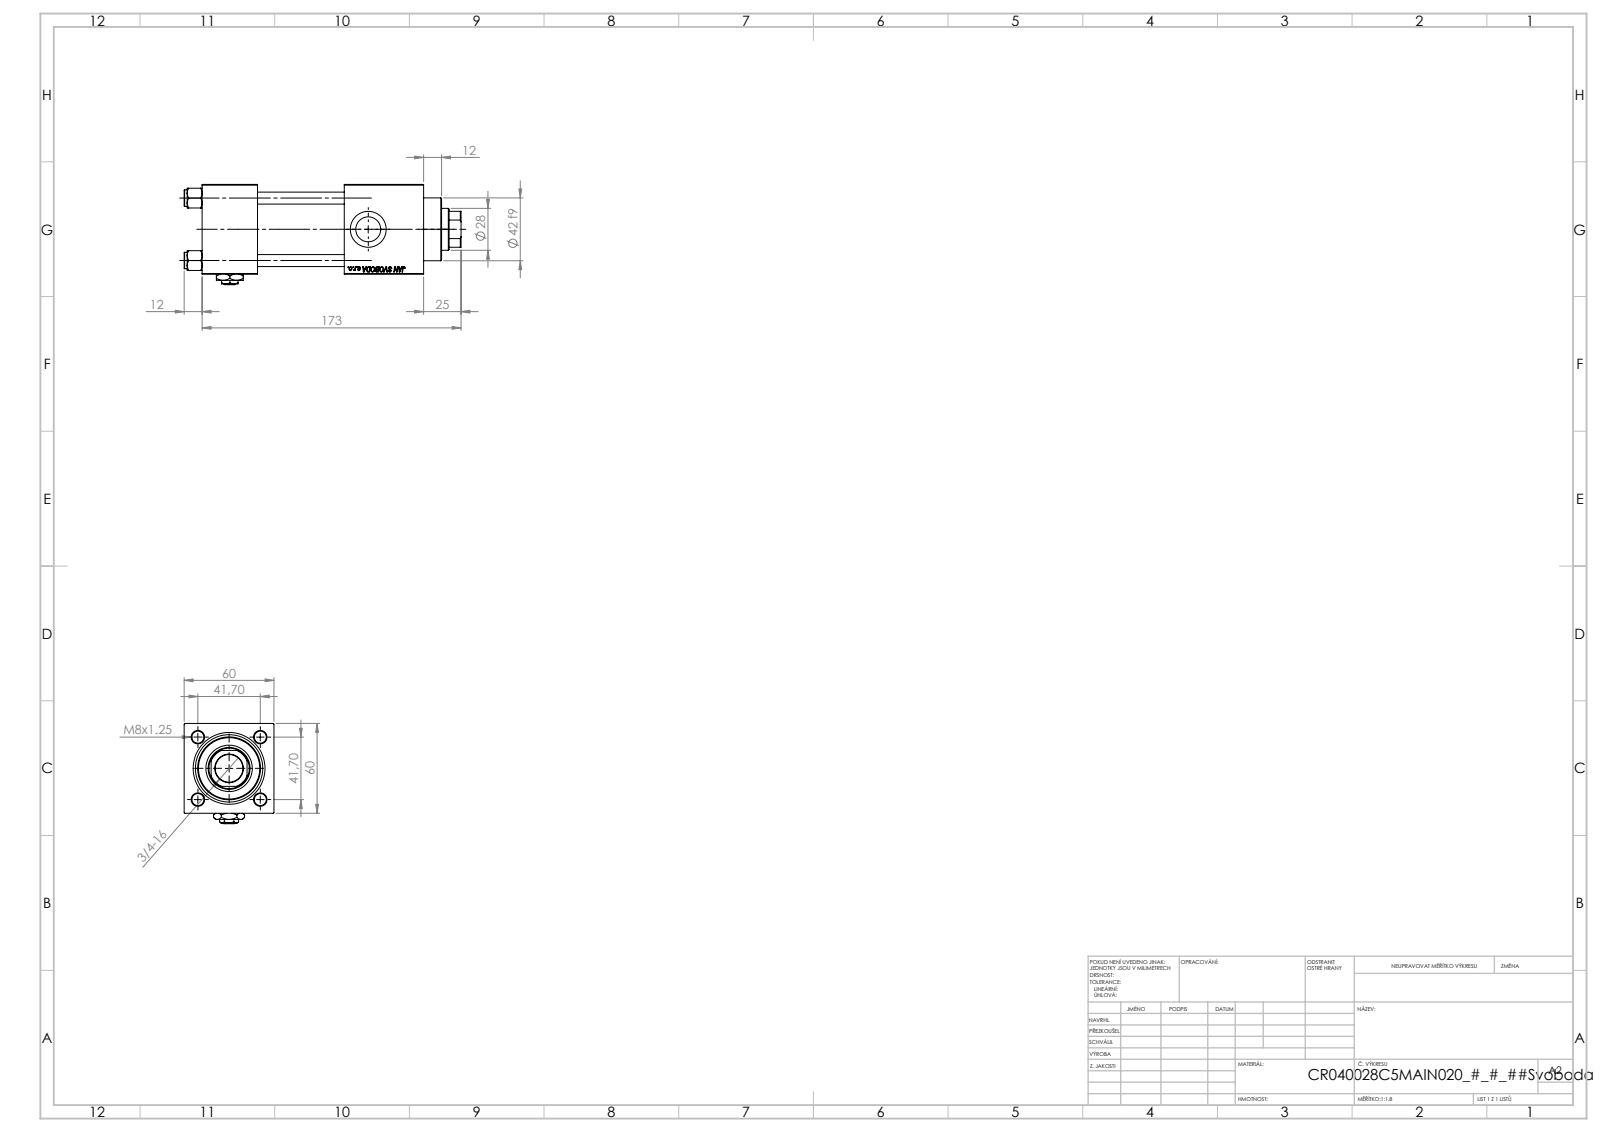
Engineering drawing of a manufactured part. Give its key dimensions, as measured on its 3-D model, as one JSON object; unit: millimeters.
{"part_name": "V215CR_C_TYCINKA; V215CR_VCP_C; V215CR_C_Body; V215_VC_A (+2 more)", "step_written_by": "SolidWorks 2019 (CONFIG_CONTROL_DESIGN)", "units": "millimeters", "bodies": {"solids": 12, "faces": 1202, "planar": 550, "cylindrical": 94, "other": 558}, "overall_size": [185, 67, 60], "volume_mm3": 422346, "surface_area_mm2": 113171, "round_holes": [[8, 4], [7, 2], [16.66, 2], [24, 2], [18.5, 1], [28, 1], [31, 1], [40, 1], [45, 1]], "round_bosses_or_shafts": [[11, 4], [46, 1], [42, 1]], "partial_cylinders_radius": [[13.5, 1]], "face_to_face_distances": [60, 37, 58, 95, 53, 119.3, 82.3, 24.3, 148, 111], "hole_center_spacings": [29.49, 41.7, 58.97]}
